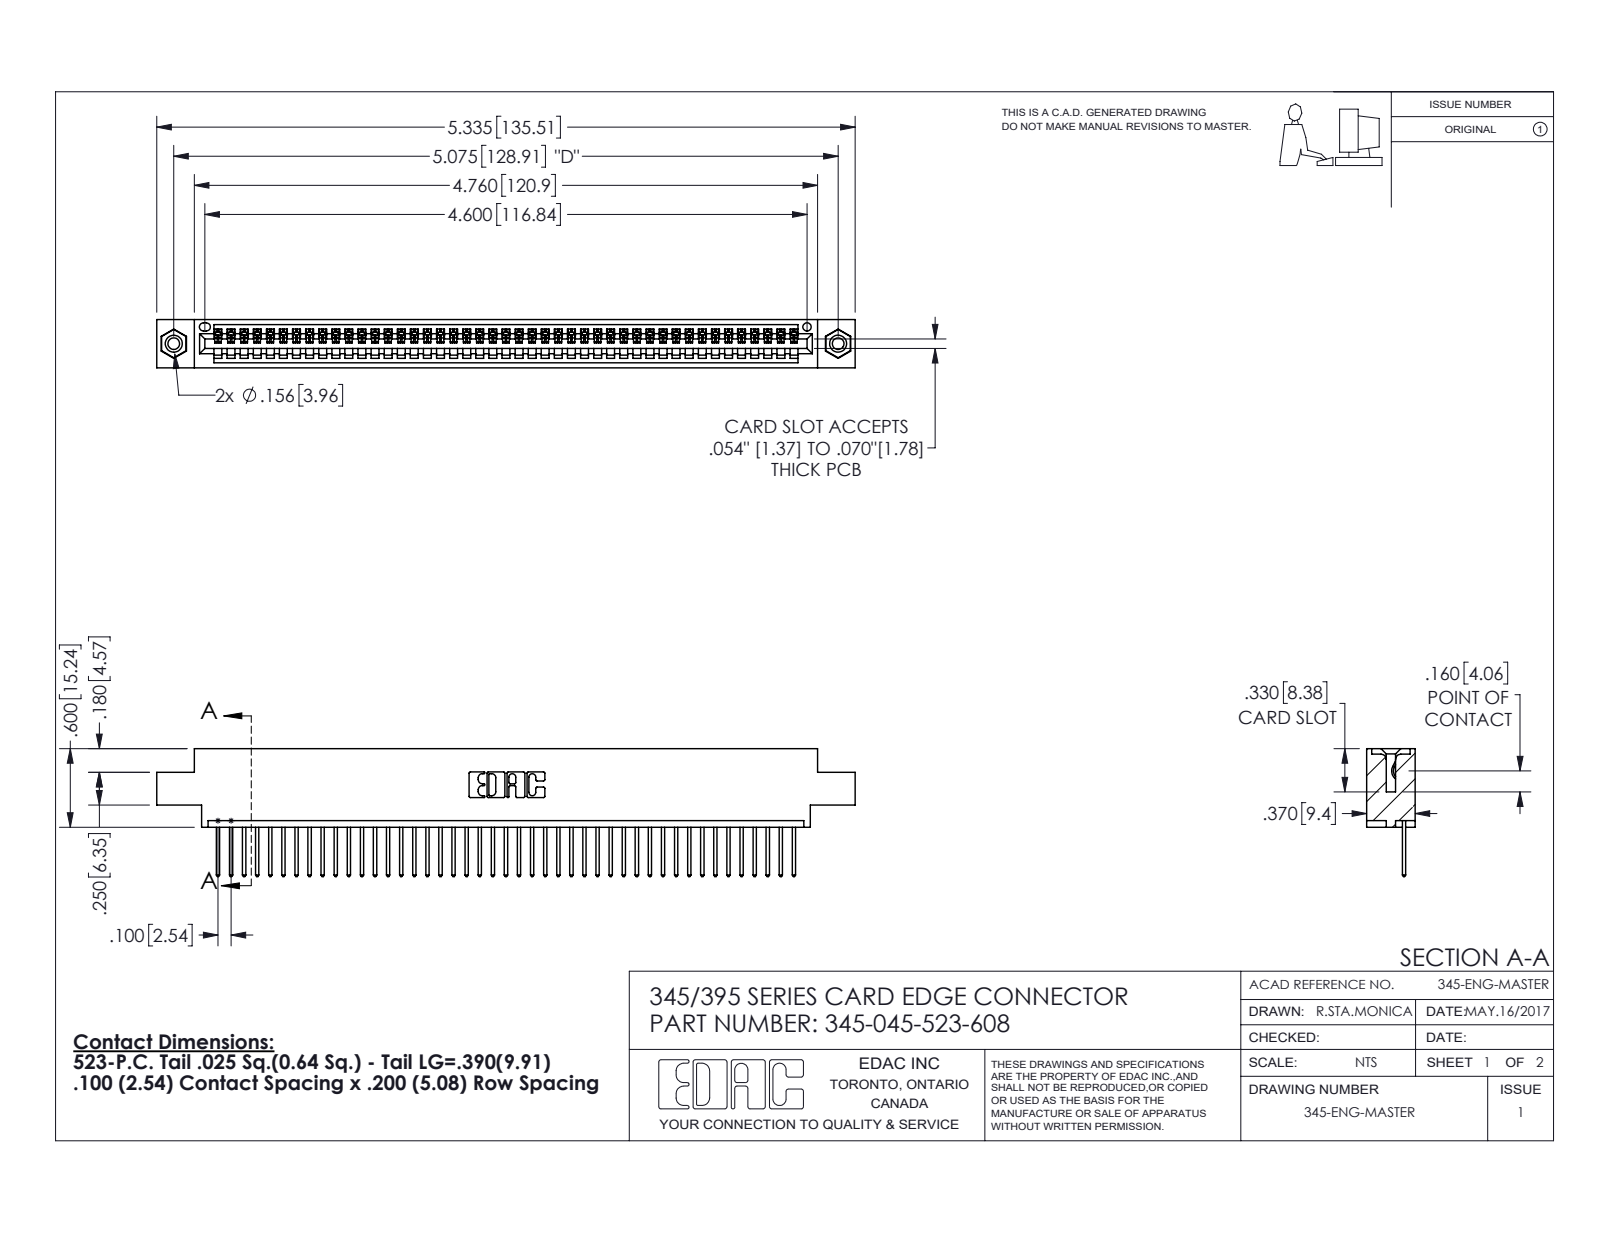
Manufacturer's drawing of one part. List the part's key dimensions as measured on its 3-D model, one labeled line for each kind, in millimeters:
Part name (STEP PRODUCT): 345 Part_0.170 Offset - 0.156 Dia-TI; 345-250-001_345-250-003-102; 345-292-001_345-293-123; 345-045-523-608
STEP written by: SolidWorks 2016 (CONFIG_CONTROL_DESIGN)
Units: millimetres
Bodies: 48 solids, 2800 faces (1916 planar, 868 cylindrical, 16 other)
Overall size (bounding box): 135.5 × 24.8 × 9.4
Volume: 12 800 mm³ · Surface area: 17 190 mm²
Round holes (diameter × count): ⌀2.3 ×2, ⌀3.2 ×2, ⌀4 ×2, ⌀1.6 ×1
Round bosses / shafts (diameter × count): ⌀3.9 ×2
Partial cylindrical surfaces — rounded edges, fillets, slot ends (radius × count): R0.2 ×90, R0.3 ×90, R0.3 ×22, R0.2 ×6, R0.8 ×6, R0.7 ×3, R0.8 ×2, R1 ×2
Main face-to-face distances: 1.8, 7.6, 9.4, 5.1, 2.5, 6.9, 0.6, 5.7, 4.4, 3.8
Hole centre spacings: 6.9, 122.9, 128.9
